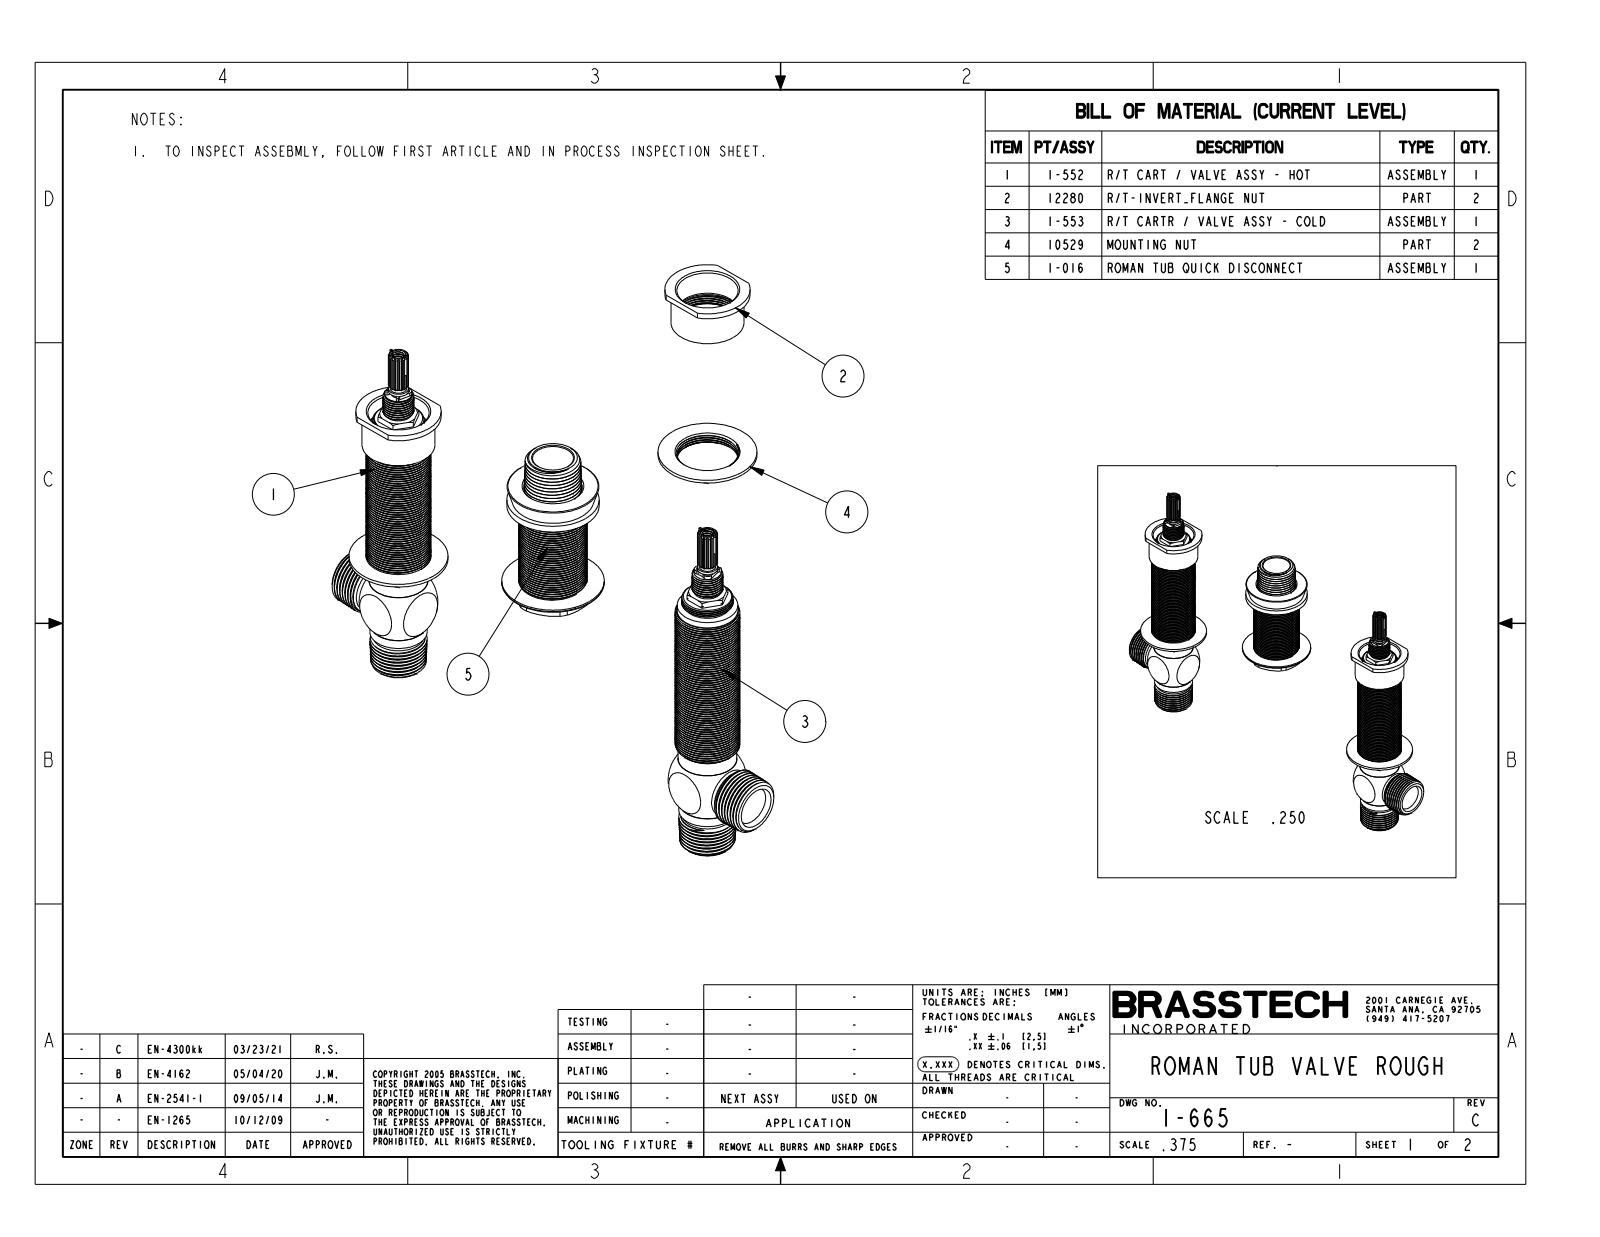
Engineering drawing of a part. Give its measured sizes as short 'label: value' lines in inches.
name: 1-665
written by: CREO PARAMETRIC BY PTC INC, 2018400 (AUTOMOTIVE_DESIGN)
unit: in
bodies: 3 solids, 1193 faces (228 planar, 514 cylindrical, 451 other)
size: 10.52 × 6.941 × 1.875
volume: 17.01 in³; area: 123.4 in²
holes: 2× ⌀0.196, 2× ⌀0.201, 2× ⌀1.12, 2× ⌀1.18, 1× ⌀0.709
bosses: 2× ⌀1.811, 2× ⌀1.335, 2× ⌀1.187, 2× ⌀1.11, 2× ⌀1.075, 2× ⌀1.047, 2× ⌀0.945, 2× ⌀0.929
rounds: 8× R0.04, 8× R0.08, 2× R0.164, 2× R0.26, 2× R0.3, 2× R0.775, 2× R0.78, 1× R0.758
face distances: 0.061, 1.503, 1.442, 3.305, 3.244, 1.802, 3.629, 3.568, 2.126, 0.324
hole spacings: 8
